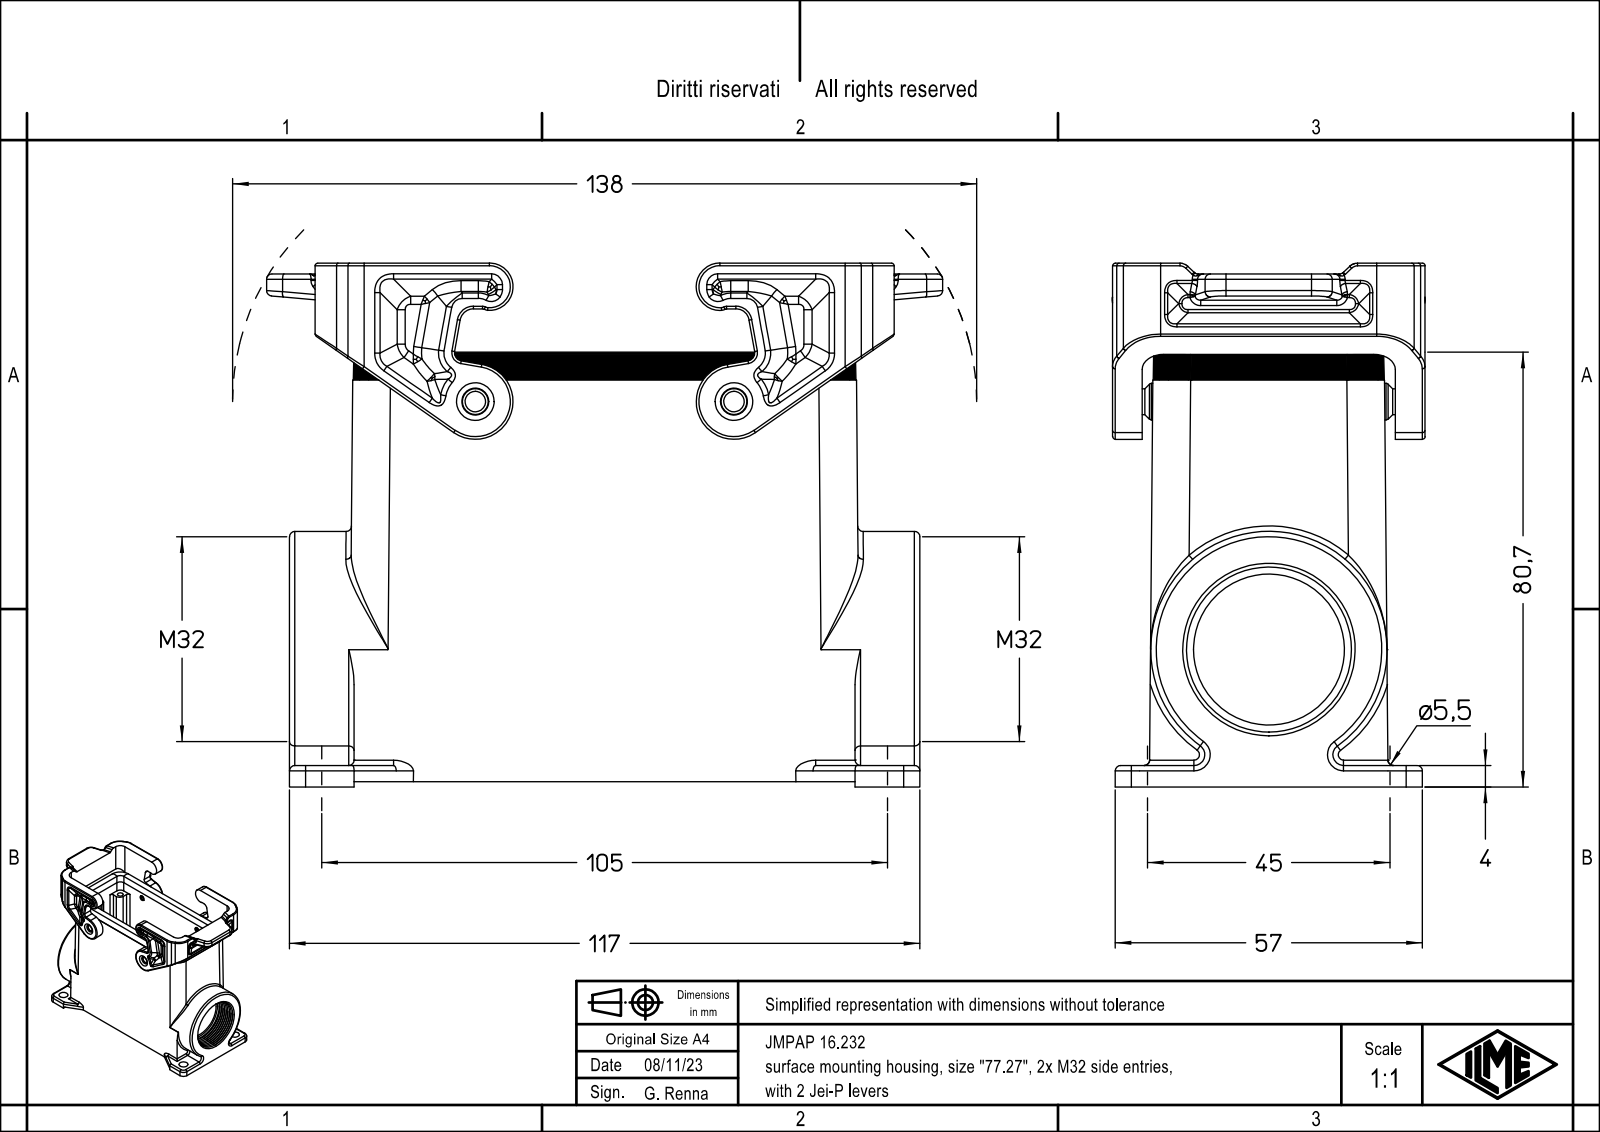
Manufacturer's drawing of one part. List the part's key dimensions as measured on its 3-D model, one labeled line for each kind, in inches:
Part name (STEP PRODUCT): JMPAP 16.232
STEP written by: Creo Elements/Direct Modeling 20.1B 02-Apr-2019 (C) Parametric Technology GmbH (AUTOMOTIVE_DESIGN)
Units: inches
Bodies: 1 solid, 866 faces (172 planar, 312 cylindrical, 382 other)
Overall size (bounding box): 4.941 × 3.827 × 2.287
Volume: 9.617 in³ · Surface area: 103.6 in²
Round holes (diameter × count): ⌀0.118 ×4, ⌀0.138 ×4, ⌀0.217 ×3, ⌀0.189 ×2, ⌀1.102 ×1, ⌀1.205 ×1
Round bosses / shafts (diameter × count): ⌀0.268 ×2, ⌀1.727 ×1
Partial cylindrical surfaces — rounded edges, fillets, slot ends (radius × count): R0.02 ×50, R0.039 ×44, R0.118 ×38, R0.079 ×26, R0.059 ×12, R0.157 ×12, R0.236 ×12, R0.276 ×10
Main face-to-face distances: 0.118, 0.039, 0.157, 1.85, 4.222, 0.384, 0.079, 0.276, 0.217, 2.067
Hole centre spacings: 0.647, 1.517, 3.61, 3.862, 1.063, 3.051, 3.231, 1.772
